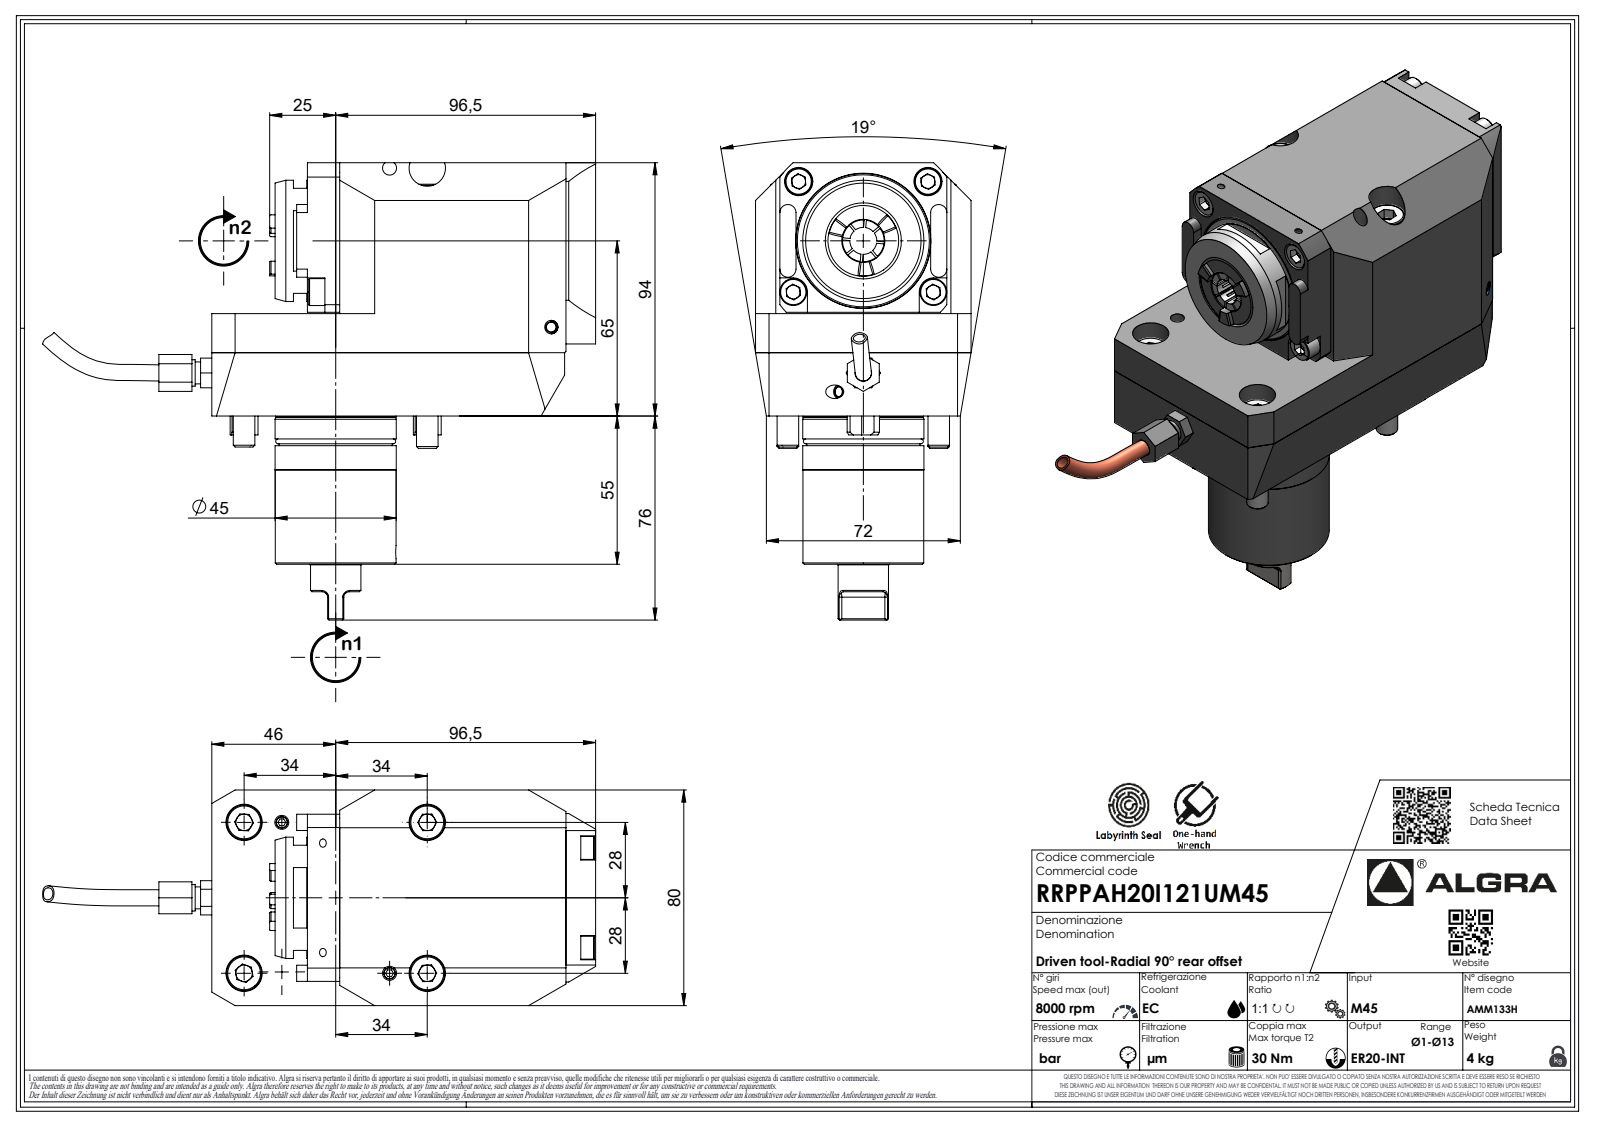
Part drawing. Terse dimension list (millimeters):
name: RRPPAH20I121UM45
written by: SolidWorks 2023 (AUTOMOTIVE_DESIGN)
unit: mm
bodies: 1 solid, 543 faces (374 planar, 81 cylindrical, 88 other)
size: 210.29 × 169.7 × 80
volume: 928 332 mm³; area: 72 814 mm²
holes: 2× ⌀13.5, 1× ⌀2.1
bosses: 4× ⌀8, 2× ⌀45, 2× ⌀13, 1× ⌀44.85, 1× ⌀44.6, 1× ⌀42, 1× ⌀18.7, 1× ⌀9.8
rounds: 7× R0.33, 7× R0.52, 7× R3.7, 6× R2, 4× R3, 4× R4, 3× R10, 2× R6
face distances: 94, 56, 38, 80, 142.5, 37.8, 93.8, 12, 23.5, 119
hole spacings: 56
